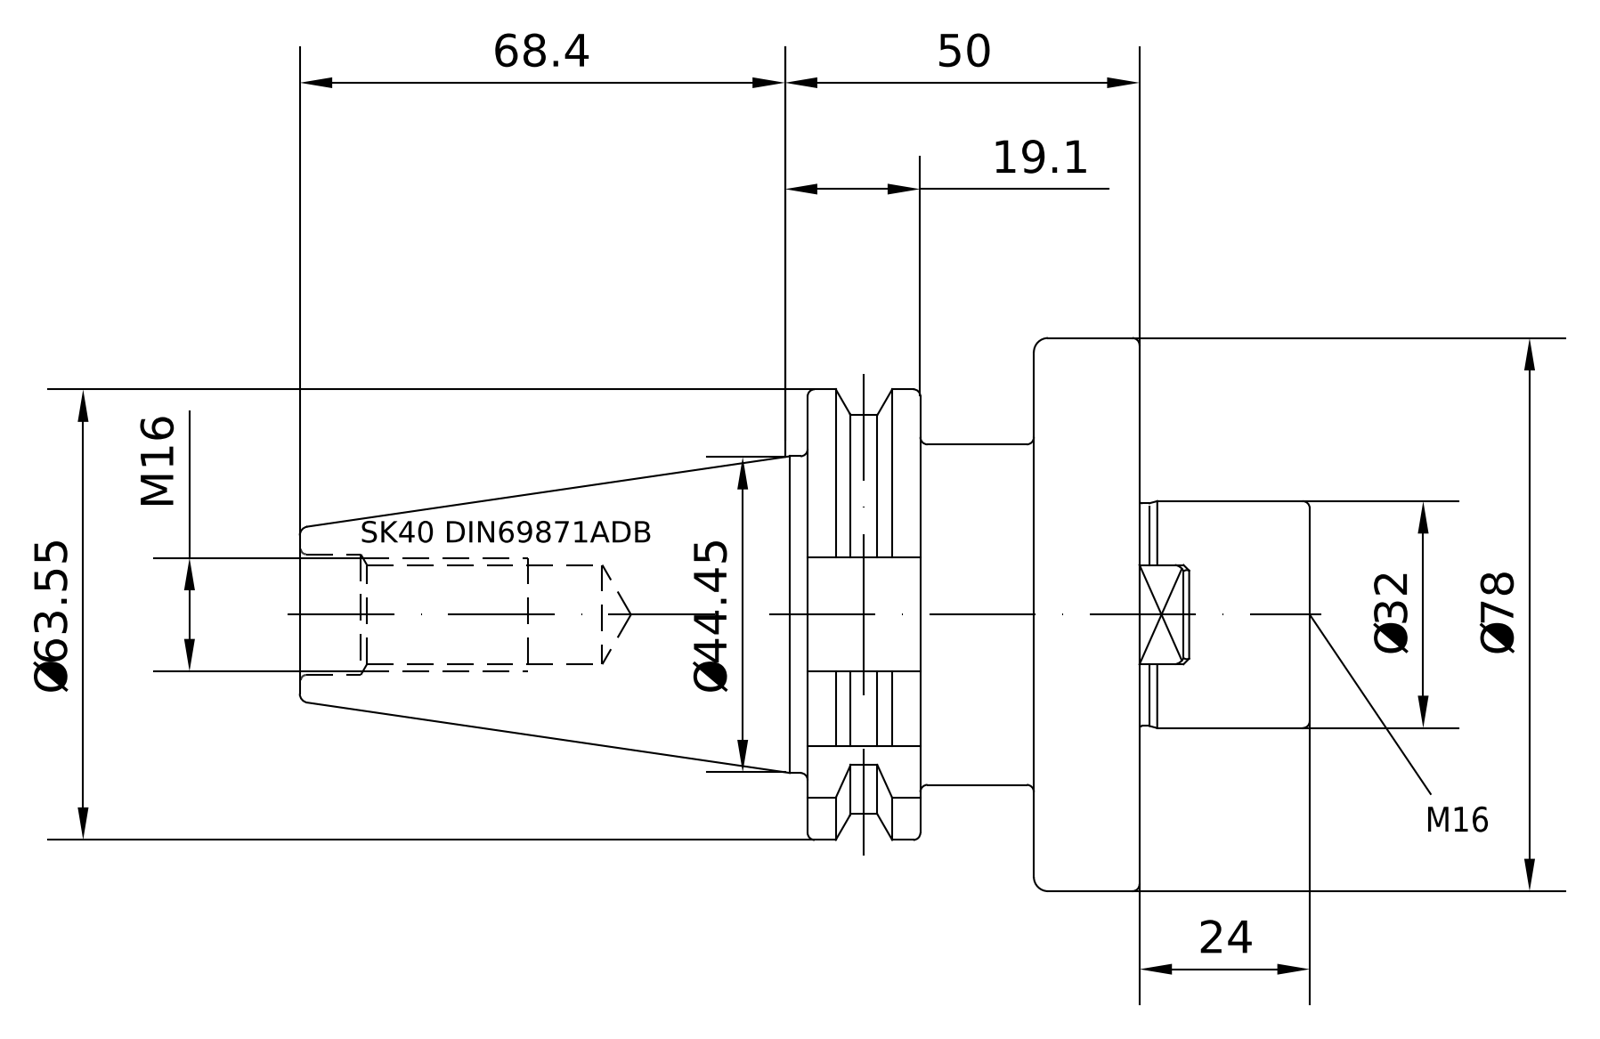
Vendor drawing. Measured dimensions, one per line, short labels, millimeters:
name: 40-350-32
written by: PRO/ENGINEER BY PARAMETRIC TECHNOLOGY CORPORATION, 2010430 (CONFIG_CONTROL_DESIGN)
unit: mm
bodies: 1 solid, 119 faces (34 planar, 33 cylindrical, 52 other)
size: 142.25 × 78 × 78
volume: 221 332 mm³; area: 38 036 mm²
holes: 1× ⌀13.84, 1× ⌀14, 1× ⌀16, 1× ⌀17.01, 1× ⌀17.5
bosses: 1× ⌀78, 1× ⌀48, 1× ⌀43.75, 1× ⌀32, 1× ⌀16.01
rounds: 5× R1.35, 1× R28, 1× R31.76
face distances: 14.95, 31.85, 46.8, 15.85, 16, 30.95, 70.8, 54.95, 38.95, 24
